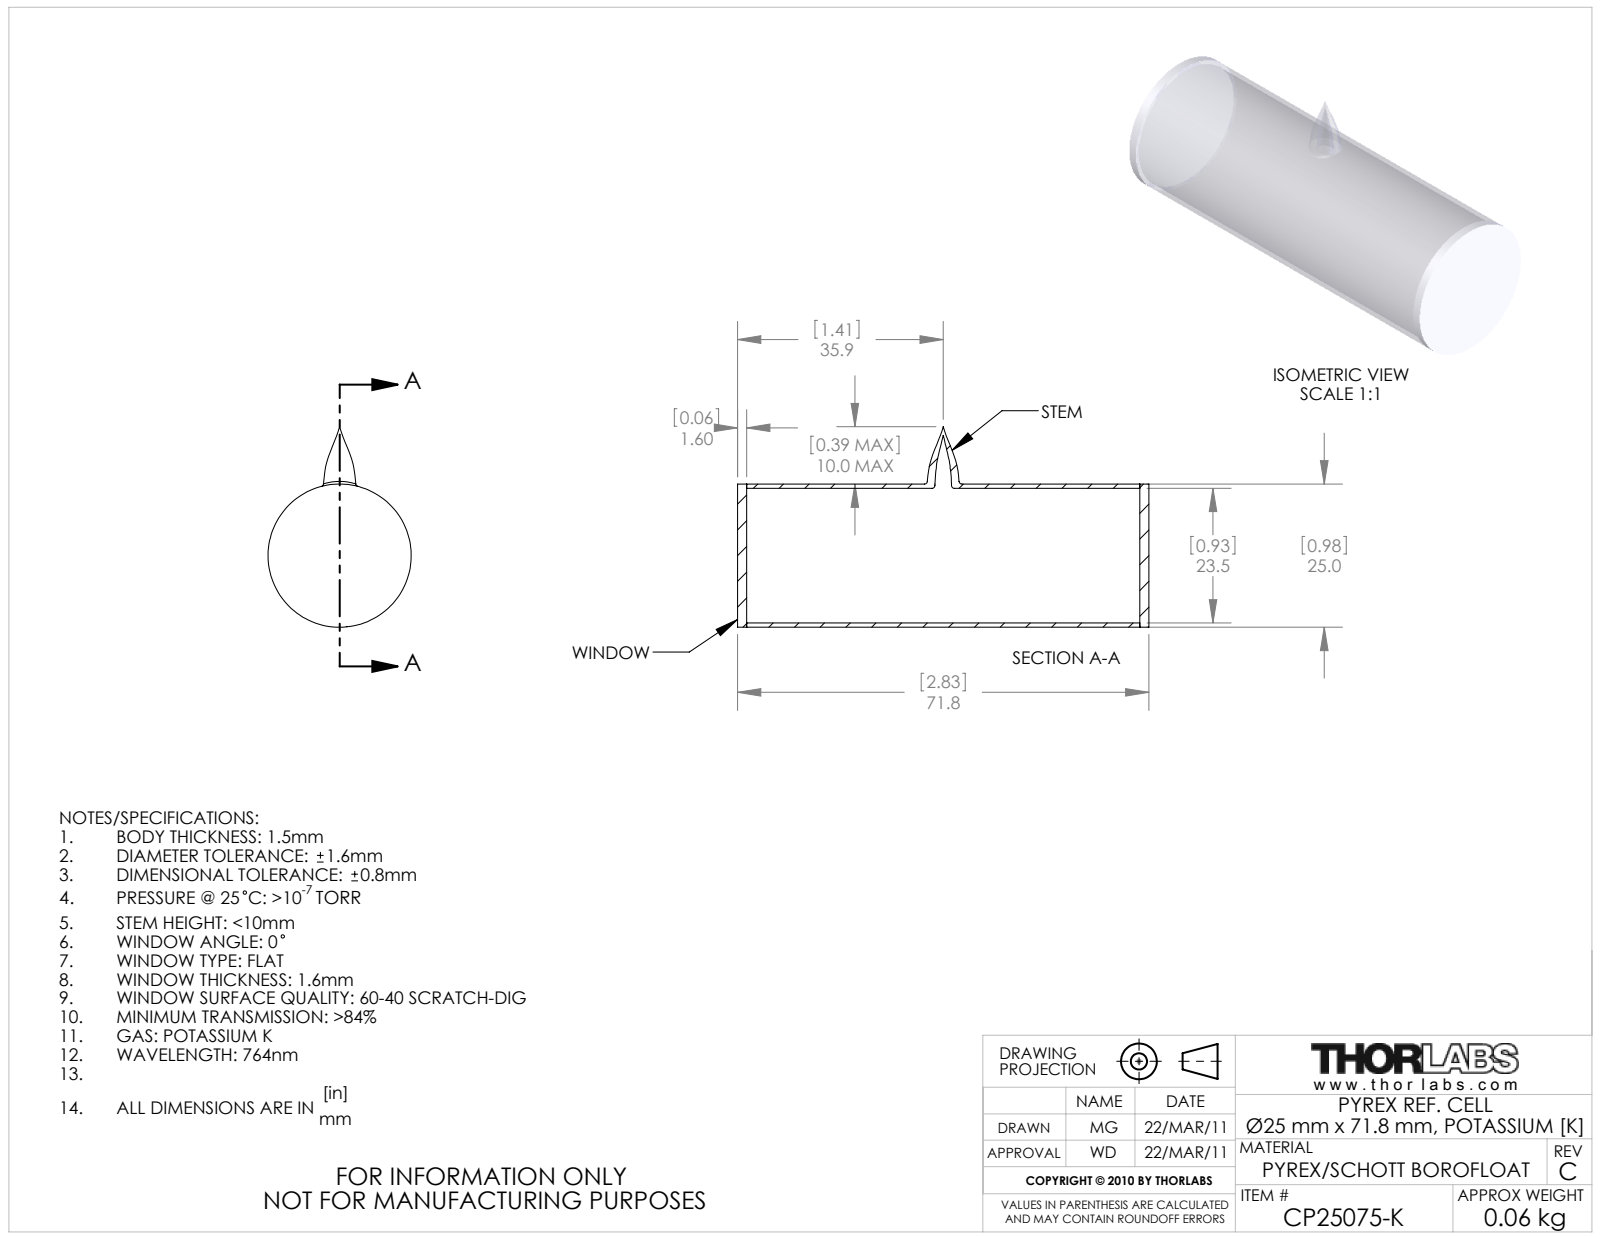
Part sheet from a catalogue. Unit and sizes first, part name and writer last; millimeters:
Units: millimetres
Overall size (bounding box): 71.84 × 35 × 25
Round holes (diameter × count): ⌀2.91 ×1, ⌀23.5 ×1
Round bosses / shafts (diameter × count): ⌀25 ×1
Main face-to-face distances: 1.6, 70.24, 68.64, 71.84
Volume: 5 577 mm³ · Surface area: 12 920 mm²
Bodies: 3 solids, 24 faces (6 planar, 10 cylindrical, 8 other)
Part name (STEP PRODUCT): 12095-E0W
STEP written by: SolidWorks 2009 (AUTOMOTIVE_DESIGN)
